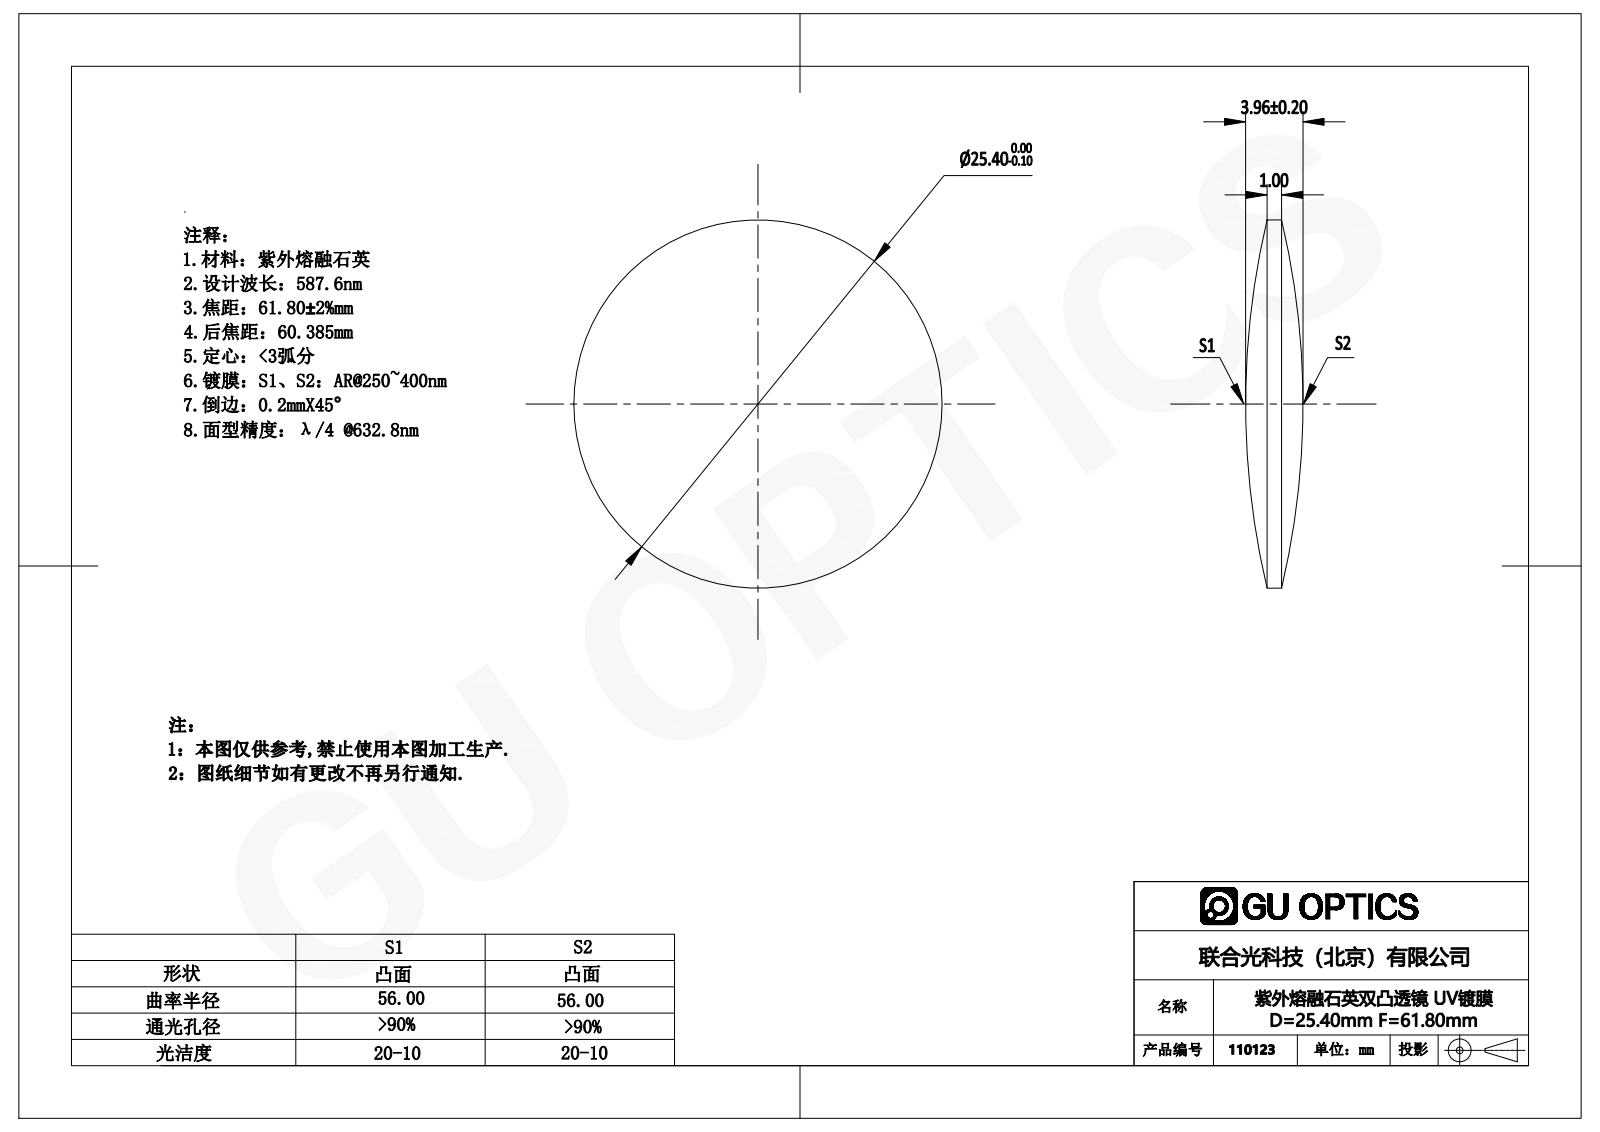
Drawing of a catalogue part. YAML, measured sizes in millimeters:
part_name: "110099"
step_written_by: "SolidWorks 2016 (CONFIG_CONTROL_DESIGN)"
units: millimeters
bodies: {solids: 1, faces: 6, planar: 0, cylindrical: 2, other: 4}
overall_size: [25.4, 25.4, 3.96]
volume: 1260
surface_area: 1107
round_bosses_or_shafts:
  - {diameter: 25.4, count: 1}
